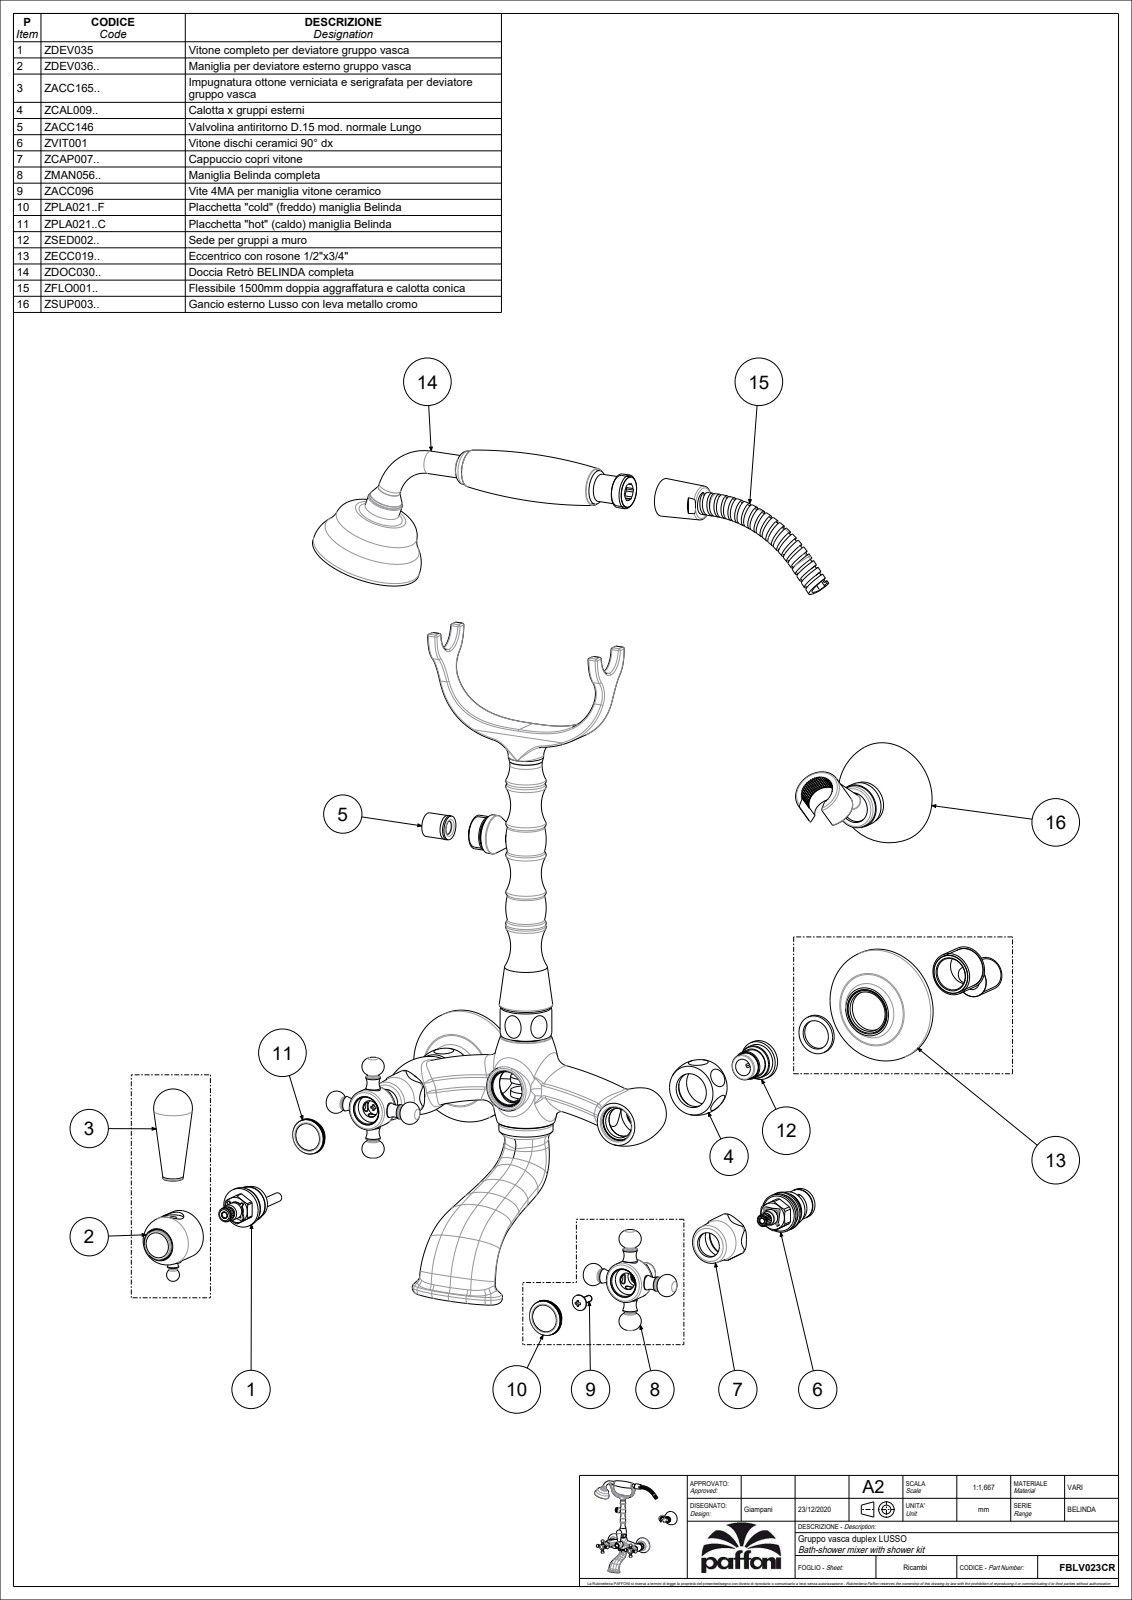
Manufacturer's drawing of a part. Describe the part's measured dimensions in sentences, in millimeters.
The part is named "FBLV023CR". Its 3-D file was written by "CREO PARAMETRIC BY PTC INC, 2020044 (CONFIG_CONTROL_DESIGN)". It is 7 solids with 2195 faces: 770 planar, 560 cylindrical and 865 other. Overall it measures 424 by 403.3 by 169.62 millimeters. Its volume is 566 432 cubic millimeters and its surface area 225 271 square millimeters. Round holes: 45 of diameter 1.2, 3 of diameter 15.5, 3 of diameter 19, 3 of diameter 21.5, 2 of diameter 16.7, 2 of diameter 18.63, 2 of diameter 21, 2 of diameter 22.8, 2 of diameter 25, 2 of diameter 25.5, 2 of diameter 68, 1 of diameter 6. Round bosses or shafts: 4 of diameter 14, 4 of diameter 7, 3 of diameter 9, 2 of diameter 70, 2 of diameter 28.14, 2 of diameter 21, 2 of diameter 13, 1 of diameter 69. Partial cylindrical surfaces (rounded edges, fillets, slot ends): 8 of radius 1, 2 of radius 3.5, 2 of radius 11, 2 of radius 20, 2 of radius 67.77, 1 of radius 4.5, 1 of radius 5, 1 of radius 10. The main face-to-face distances are 21, 27, 38.5, 1, 17.5, 48, 23.5, 29.5, 18.5, 157. The hole center spacings are 38.08, 33.94, 46.36, 12.42, 24, 41.57, 44.34, 6.27.
